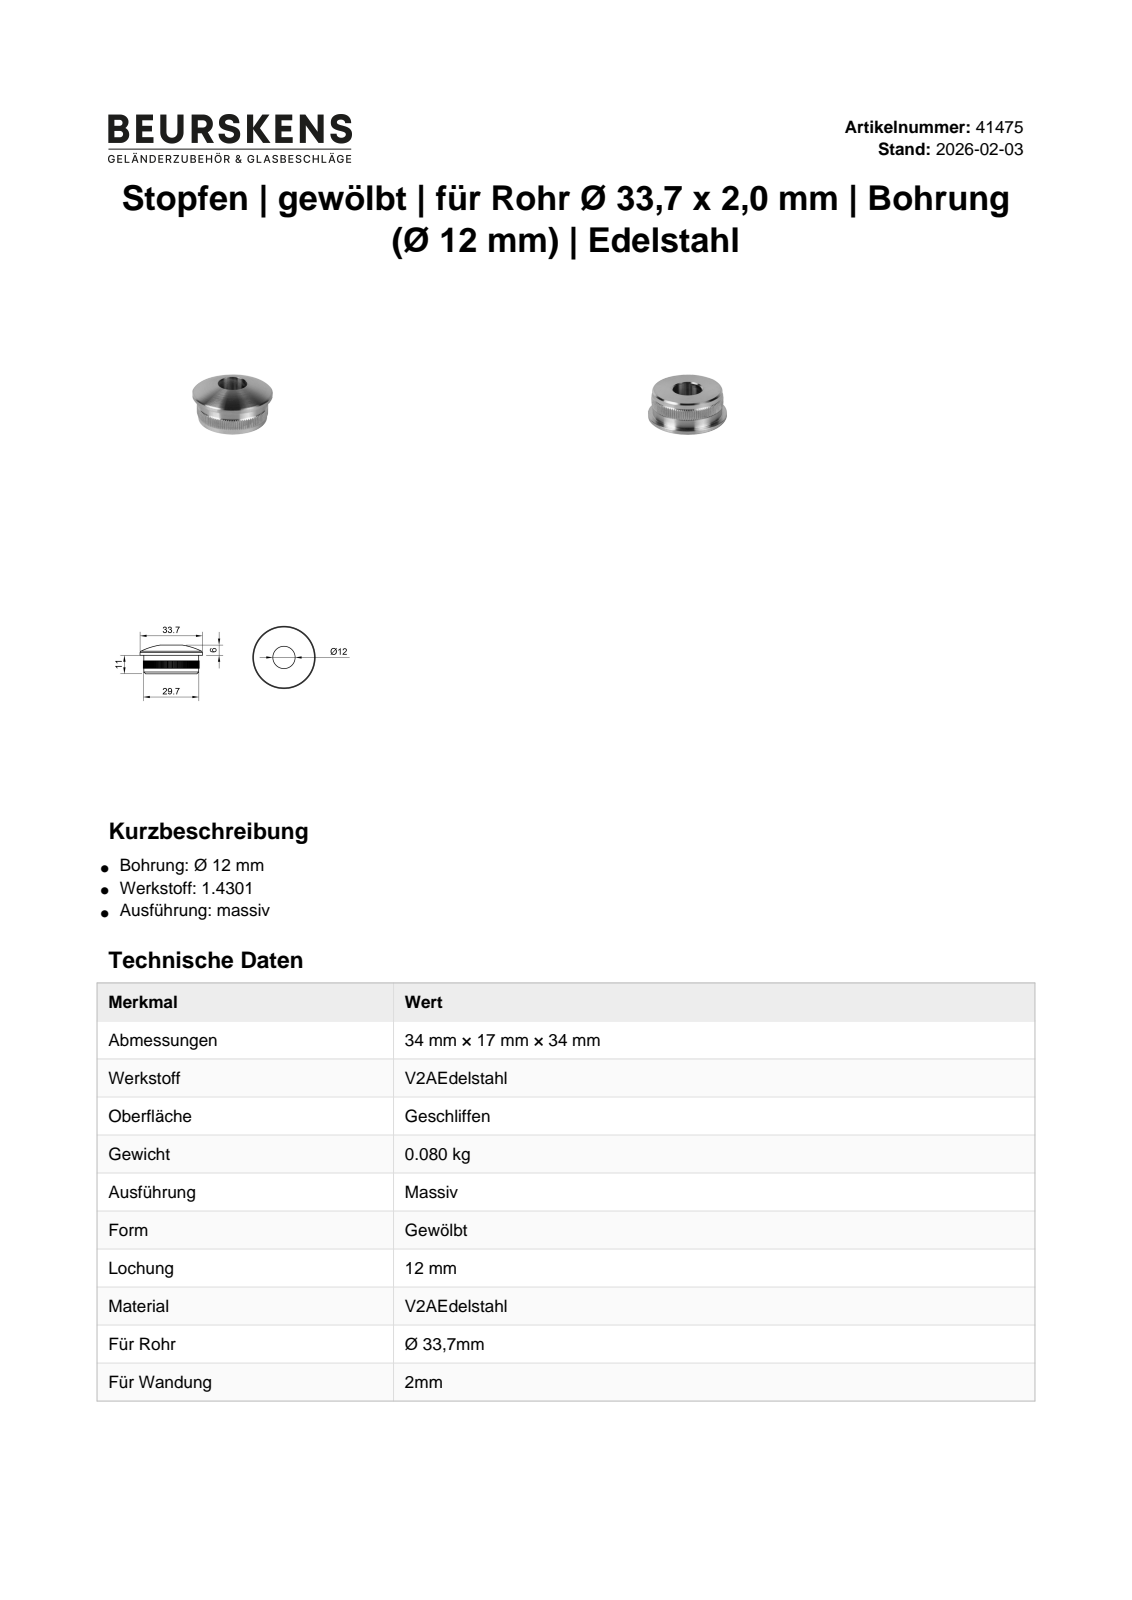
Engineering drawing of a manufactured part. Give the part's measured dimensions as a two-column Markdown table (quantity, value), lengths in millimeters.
| quantity | value |
| --- | --- |
| part name | 41475 |
| STEP written by | Autodesk Inventor 2022 (AUTOMOTIVE_DESIGN) |
| units | millimeters |
| bodies | 1 solid, 291 faces (4 planar, 284 cylindrical, 3 other) |
| overall size | 33.7 × 33.7 × 15.51 |
| volume | 8 728 mm³ |
| surface area | 3 398 mm² |
| round holes (diameter × count) | 12.05 × 1 |
| round bosses / shafts (diameter × count) | 33.7 × 1, 29.6 × 1 |
| partial cylindrical surfaces (radius × count) | 0.12 × 140, 15.1 × 1 |
| main face-to-face distances | 10, 3, 7, 4 |
